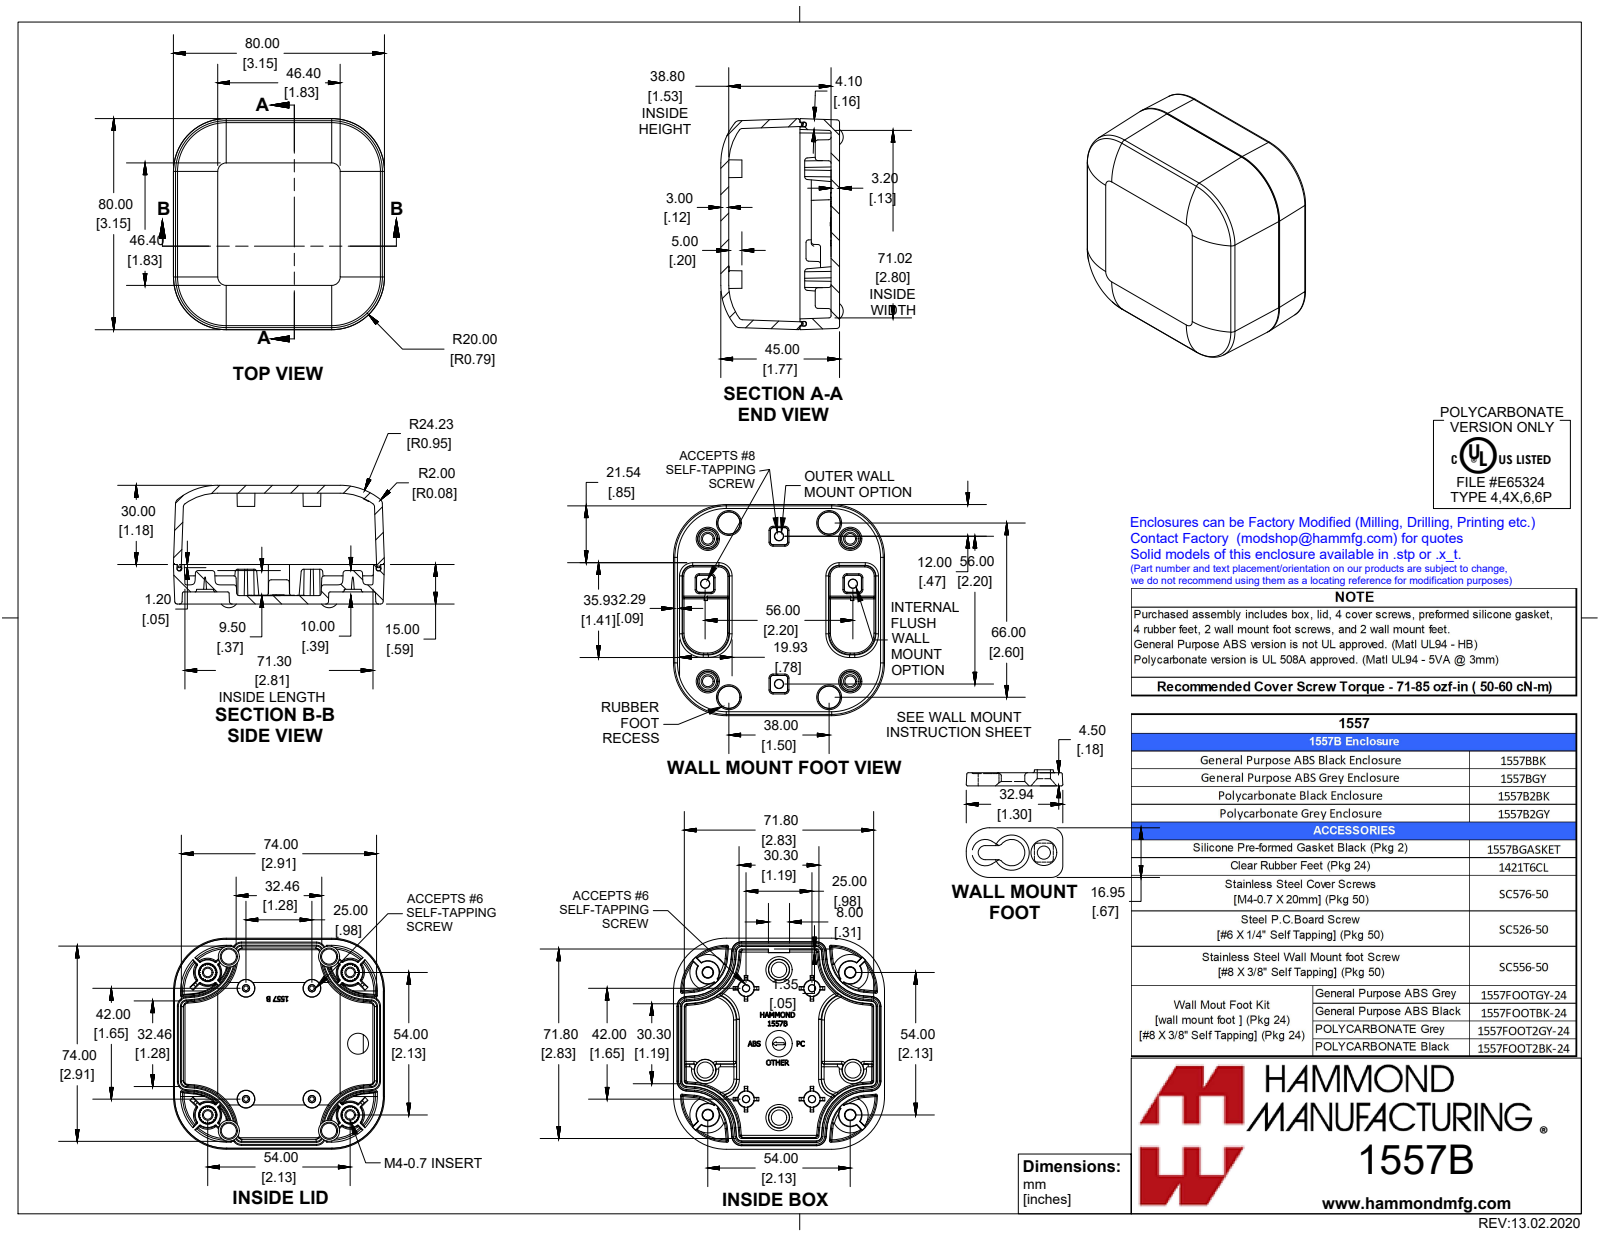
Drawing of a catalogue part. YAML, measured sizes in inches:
part_name: "1557B TOP; 1557B Bottom; SC576 (screw M4-0.7X 20mm PN); Wall Mount Foot (+5 more)"
step_written_by: "SolidWorks 2019 (CONFIG_CONTROL_DESIGN)"
units: inches
bodies: {solids: 19, faces: 2468, planar: 810, cylindrical: 471, other: 1187}
overall_size: [4.289, 3.15, 1.949]
volume: 5.93
surface_area: 113.3
round_holes:
  - {diameter: 0.128, count: 4}
  - {diameter: 0.177, count: 2}
round_bosses_or_shafts:
  - {diameter: 0.071, count: 12}
  - {diameter: 0.313, count: 4}
  - {diameter: 0.25, count: 4}
  - {diameter: 0.218, count: 4}
  - {diameter: 0.21, count: 4}
  - {diameter: 0.153, count: 4}
  - {diameter: 0.135, count: 4}
  - {diameter: 0.303, count: 2}
partial_cylinders:
  - {radius: 0.02, count: 104}
  - {radius: 0.039, count: 53}
  - {radius: 0.079, count: 12}
  - {radius: 0.012, count: 8}
  - {radius: 0.059, count: 8}
  - {radius: 0.157, count: 8}
  - {radius: 0.315, count: 6}
  - {radius: 0.836, count: 4}
face_to_face_distances: [0.118, 3.029, 3.146, 0.118, 1.772, 1.654, 0.126, 1.646, 1.528, 0.465]
hole_center_spacings: [1.064, 2.126, 2.412, 3.007, 2.205]
